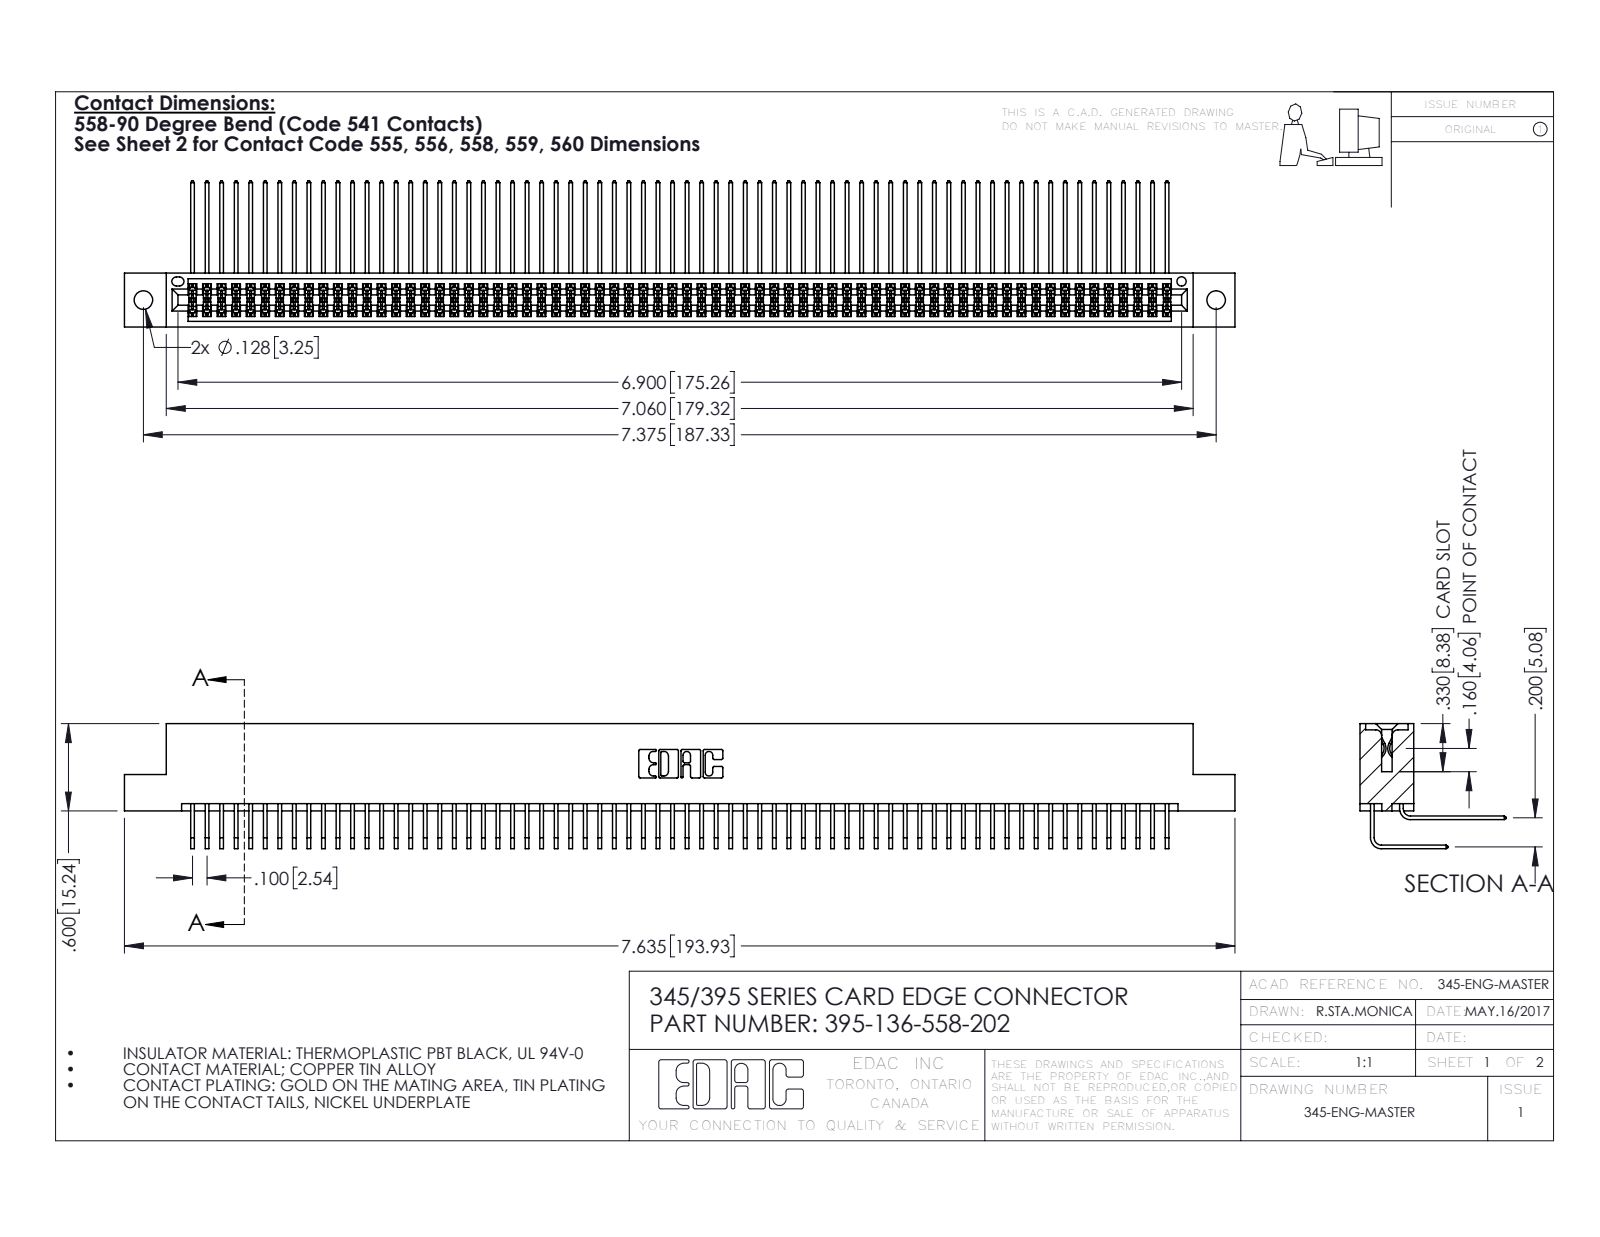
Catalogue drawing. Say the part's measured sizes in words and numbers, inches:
The part is named "345-292-001_558 Tail - 2; 345-292-001_558 559 Tail - 1; 345 Part_Flush Mounting Lugs - 0.128 Dia; 395-136-558-202". Its 3-D file was written by "SolidWorks 2016 (CONFIG_CONTROL_DESIGN)". It is 137 solids with 7198 faces: 4840 planar, 2358 cylindrical and 0 other. Overall it measures 7.635 by 1.005 by 0.859 inches. Its volume is 1.21 cubic inches and its surface area 51.5 square inches. Round holes: 2 of diameter 0.128, 1 of diameter 0.064. Partial cylindrical surfaces (rounded edges, fillets, slot ends): 271 of radius 0.006, 22 of radius 0.01, 6 of radius 0.007, 6 of radius 0.031, 3 of radius 0.026, 2 of radius 0.014, 2 of radius 0.019, 2 of radius 0.022. The main face-to-face distances are 0.072, 0.298, 0.2, 0.37, 0.098, 0.272, 0.025, 0.225, 0.025, 0.175. The hole center spacings are 0.27, 7.139, 7.375.
